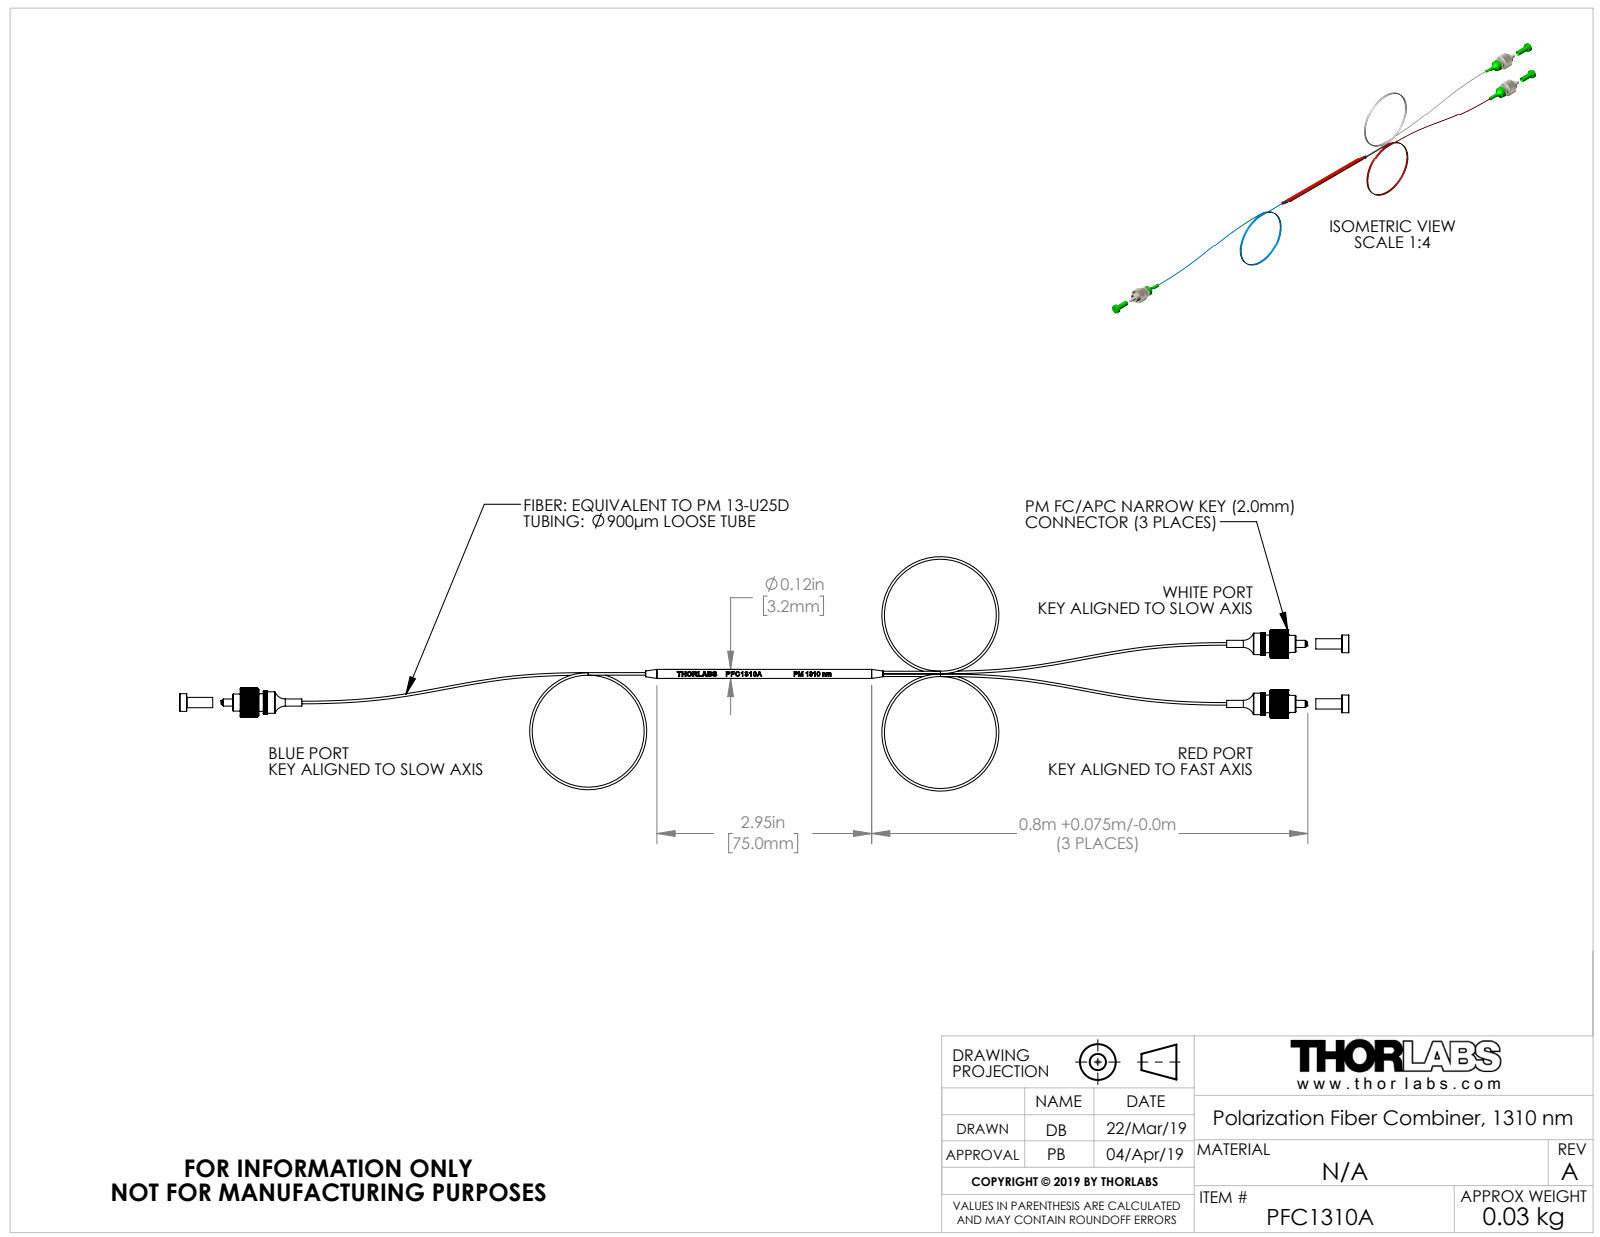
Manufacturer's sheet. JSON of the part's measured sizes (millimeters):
{"part_name": "DWG1751_48-2mm; PANDA 1310_60; DWG1631_75mm; DWG1528 (+8 more)", "step_written_by": "SolidWorks 2018 (CONFIG_CONTROL_DESIGN)", "units": "millimeters", "bodies": {"solids": 32, "faces": 2624, "planar": 1277, "cylindrical": 891, "other": 456}, "overall_size": [408.3, 81.85, 14], "volume_mm3": 3285, "surface_area_mm2": 13610, "round_holes": [[0.5, 6], [0.9, 3], [0.95, 3], [1, 3], [2.5, 3], [2.8, 3], [3.36, 3], [4.38, 3], [4.4, 3], [5.08, 3], [5.55, 3], [6.1, 3]], "round_bosses_or_shafts": [[7.5, 3], [7.07, 3], [6.17, 3], [6.08, 3], [5.95, 3], [5.38, 3], [4.85, 3], [3.6, 3]], "partial_cylinders_radius": [[0.5, 6], [0.75, 3], [1.55, 3], [2.26, 3], [3.98, 3], [5, 3], [0.45, 2], [1, 1]], "face_to_face_distances": [6.86, 6.85, 2, 1.43, 4.97, 349.97, 1.54, 2.97, 3.43, 27.68], "hole_center_spacings": [10.2, 10.67, 11.13, 0.47, 0.48, 0.95, 4.03, 9.74]}
